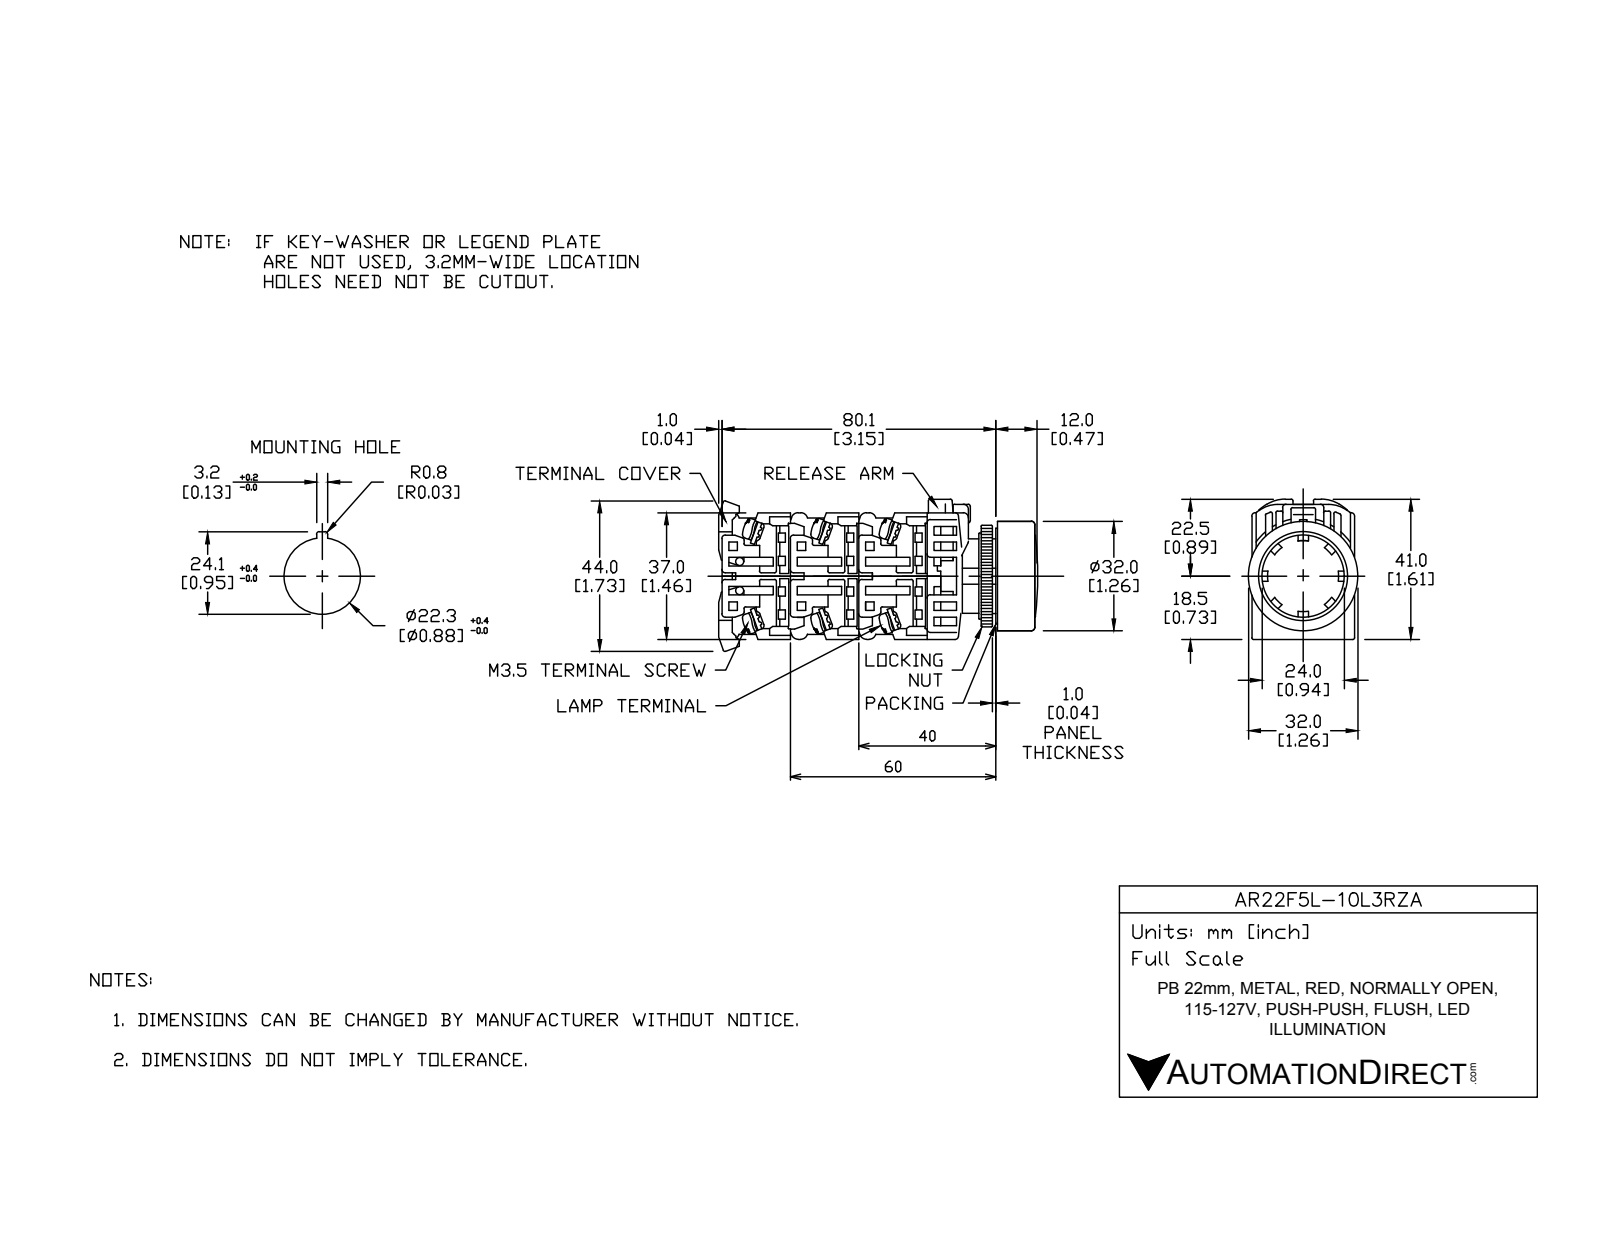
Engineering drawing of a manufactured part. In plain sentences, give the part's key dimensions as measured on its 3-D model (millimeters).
The part is named "AR22F5L-10L3RZA". Its 3-D file was written by "SolidWorks 2017 (AUTOMOTIVE_DESIGN)". It is 16 solids with 451 faces: 317 planar, 99 cylindrical and 35 other. Overall it measures 72.75 by 43.81 by 32 millimeters. Its volume is 47 521 cubic millimeters and its surface area 25 721 square millimeters. Round holes: 1 of diameter 21.8, 1 of diameter 22, 1 of diameter 25, 1 of diameter 31. Round bosses or shafts: 4 of diameter 5, 1 of diameter 32, 1 of diameter 30.5, 1 of diameter 29.8, 1 of diameter 24, 1 of diameter 23.8, 1 of diameter 21.75, 1 of diameter 17. Partial cylindrical surfaces (rounded edges, fillets, slot ends): 32 of radius 0.5, 8 of radius 1.75, 4 of radius 5, 2 of radius 4, 1 of radius 16.59, 1 of radius 17.59. The main face-to-face distances are 1, 18, 29, 20, 28.5, 3, 2, 21, 0.35, 7.5.
